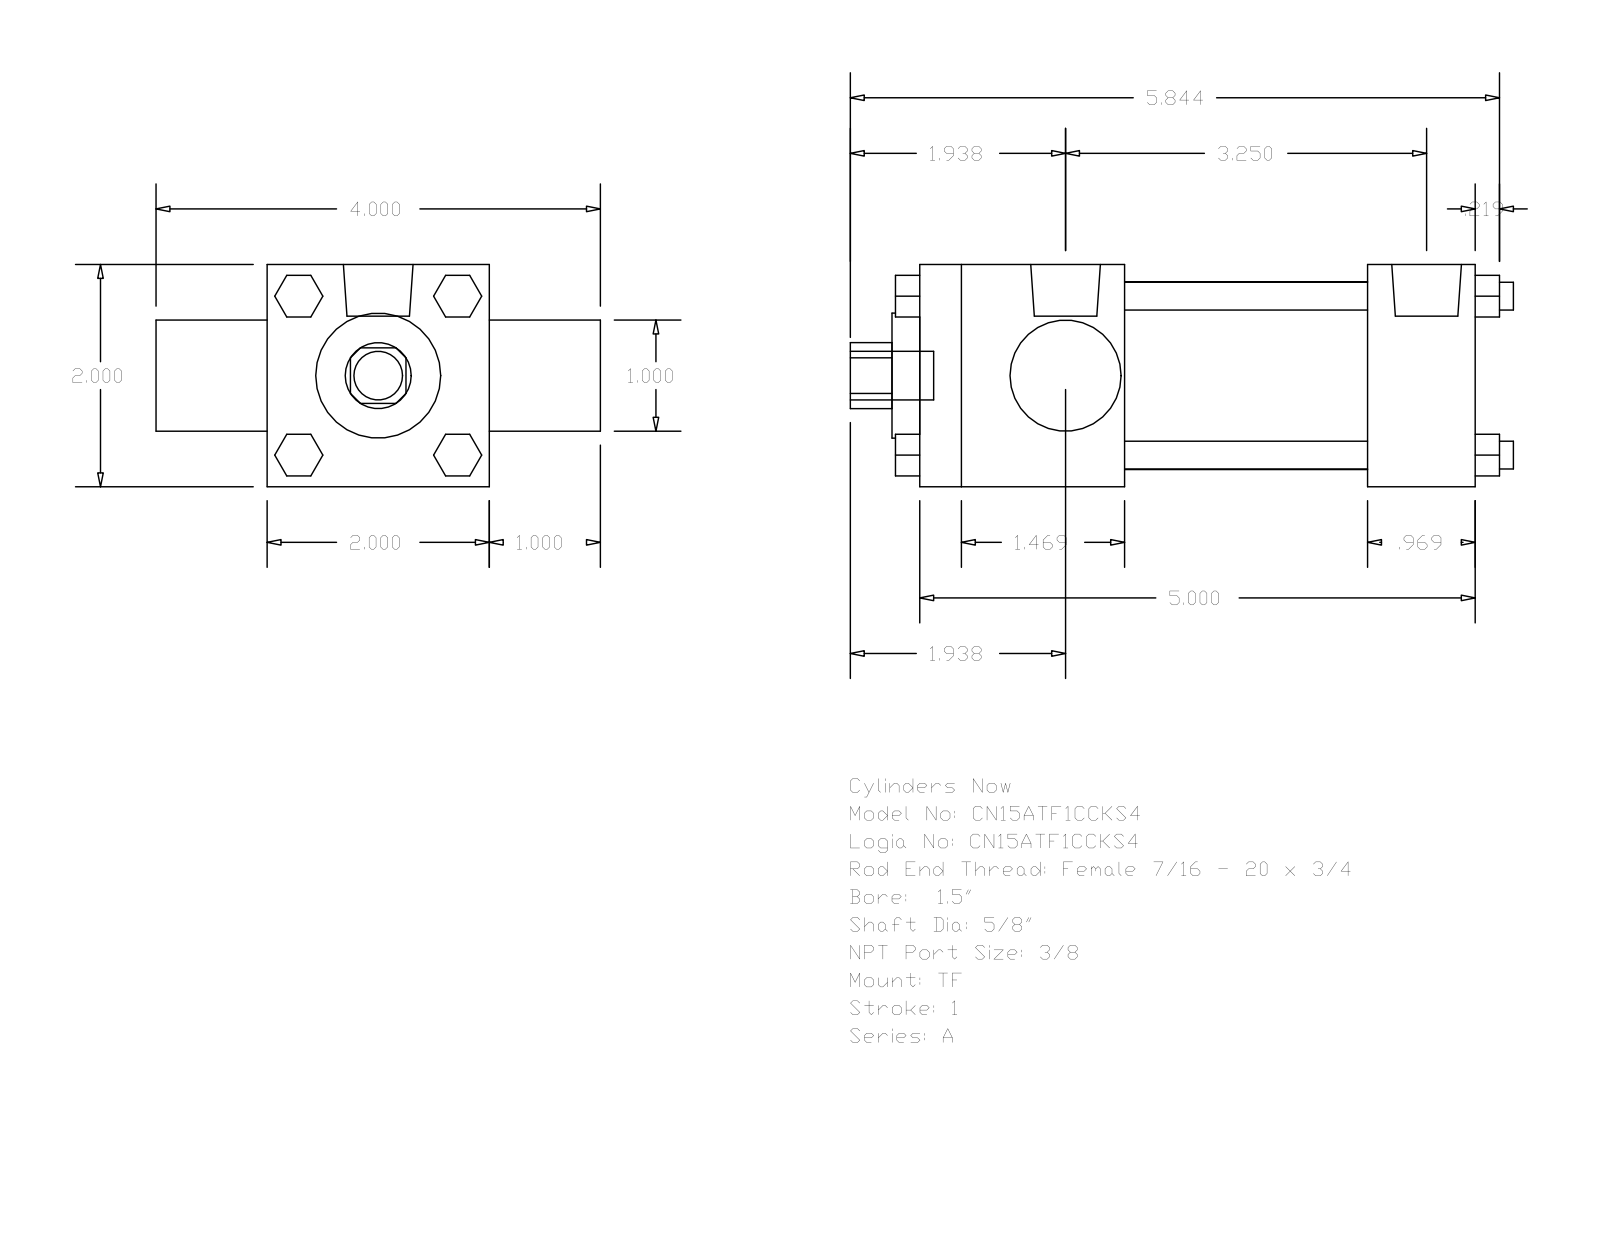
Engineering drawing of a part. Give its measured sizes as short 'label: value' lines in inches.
name: A_TF__0150_0.625
written by: GSSL Pune (CONFIG_CONTROL_DESIGN)
unit: in
bodies: 0 solids, 120 faces (92 planar, 28 cylindrical, 0 other)
size: 5.969 × 4 × 2
holes: 1× ⌀0.625, 1× ⌀1, 1× ⌀1.125, 1× ⌀1.69
bosses: 4× ⌀0.25, 3× ⌀0.219, 2× ⌀0.627, 1× ⌀0.437
rounds: 1× R0.297
face distances: 2, 5, 1, 3, 1.844, 4.031, 2.187, 3.156, 0.969, 0.375
